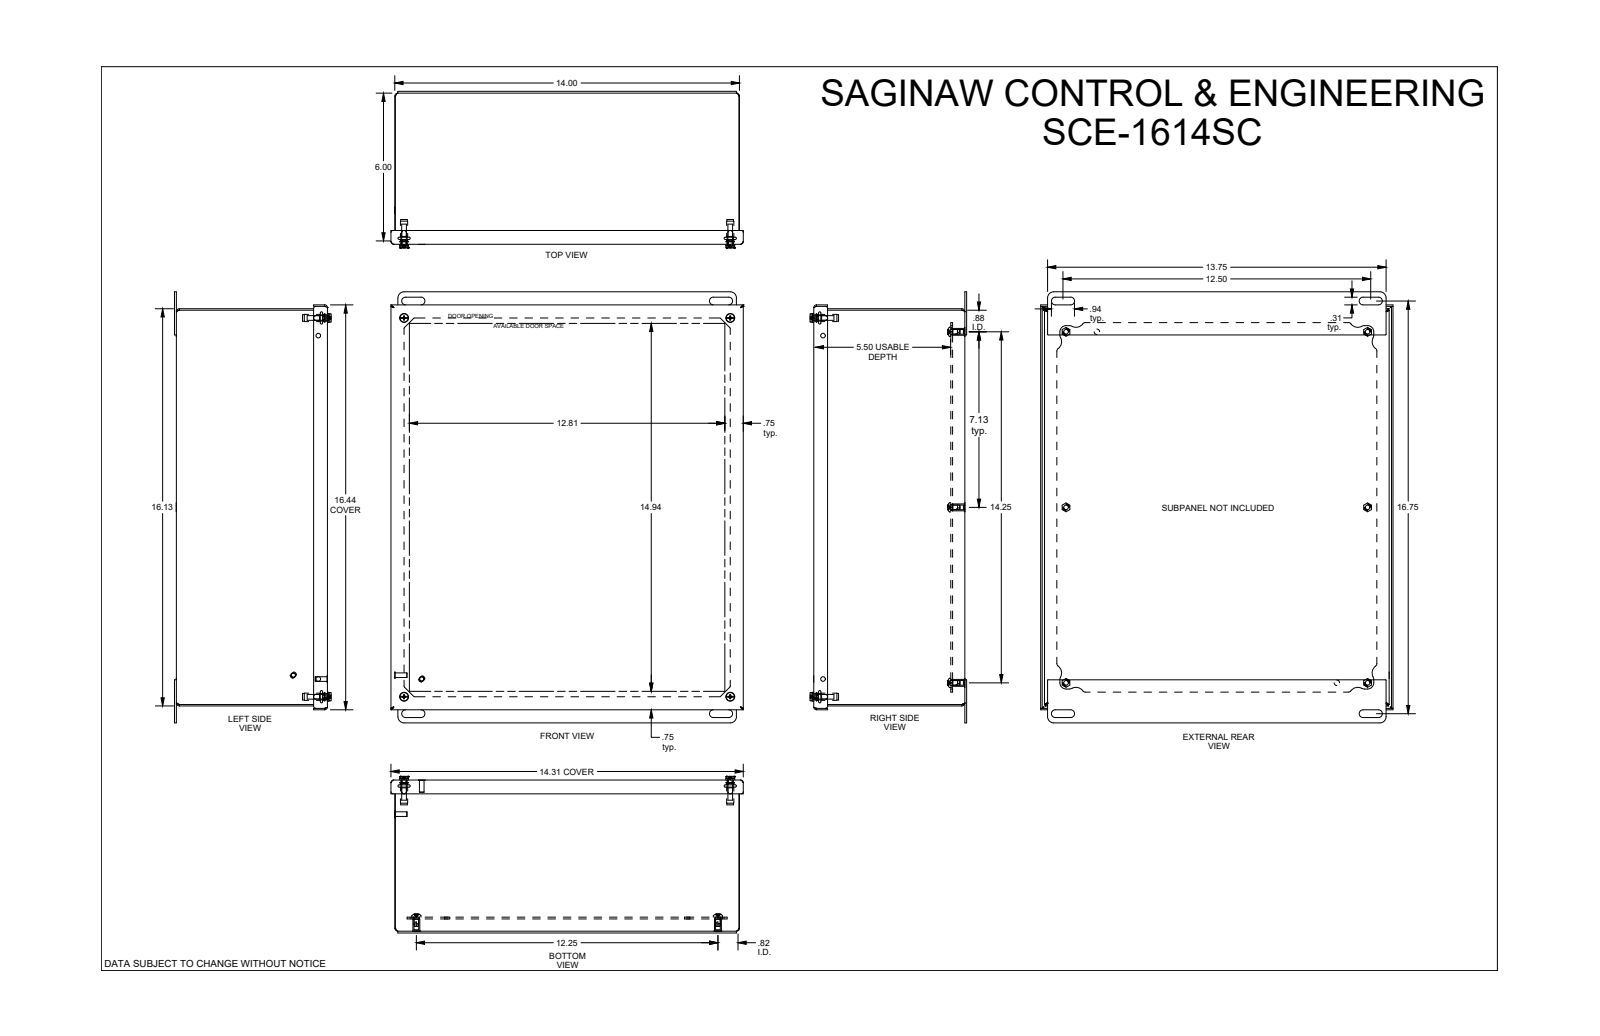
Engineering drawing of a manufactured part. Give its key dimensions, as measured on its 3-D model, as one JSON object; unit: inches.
{"part_name": "SCE-1614SC", "step_written_by": "SolidWorks 2019 (AUTOMOTIVE_DESIGN)", "units": "inches", "bodies": {"solids": 32, "faces": 927, "planar": 386, "cylindrical": 219, "other": 322}, "overall_size": [17.5, 14.313, 6.361], "volume_in3": 71.77, "surface_area_in2": 2284, "round_holes": [[0.19, 10], [0.25, 10], [0.22, 4], [0.266, 4], [0.281, 4], [0.317, 4], [0.187, 2], [0.218, 2], [0.193, 1]], "round_bosses_or_shafts": [[0.188, 12], [0.373, 6], [0.28, 6], [0.437, 4], [0.362, 4], [0.34, 4], [0.334, 4], [0.292, 4]], "partial_cylinders_radius": [[0.125, 16], [0.25, 16], [0.06, 12], [0.005, 8], [0.05, 8], [0.063, 8], [0.156, 8], [0.255, 8]], "face_to_face_distances": [0.06, 6.075, 6.135, 6.015, 5.505, 0.075, 0.57, 0.51, 5.565, 0.495], "hole_center_spacings": [14.821, 19.544, 0.753, 15.375, 12.763, 13.25, 14.889, 20.297]}
